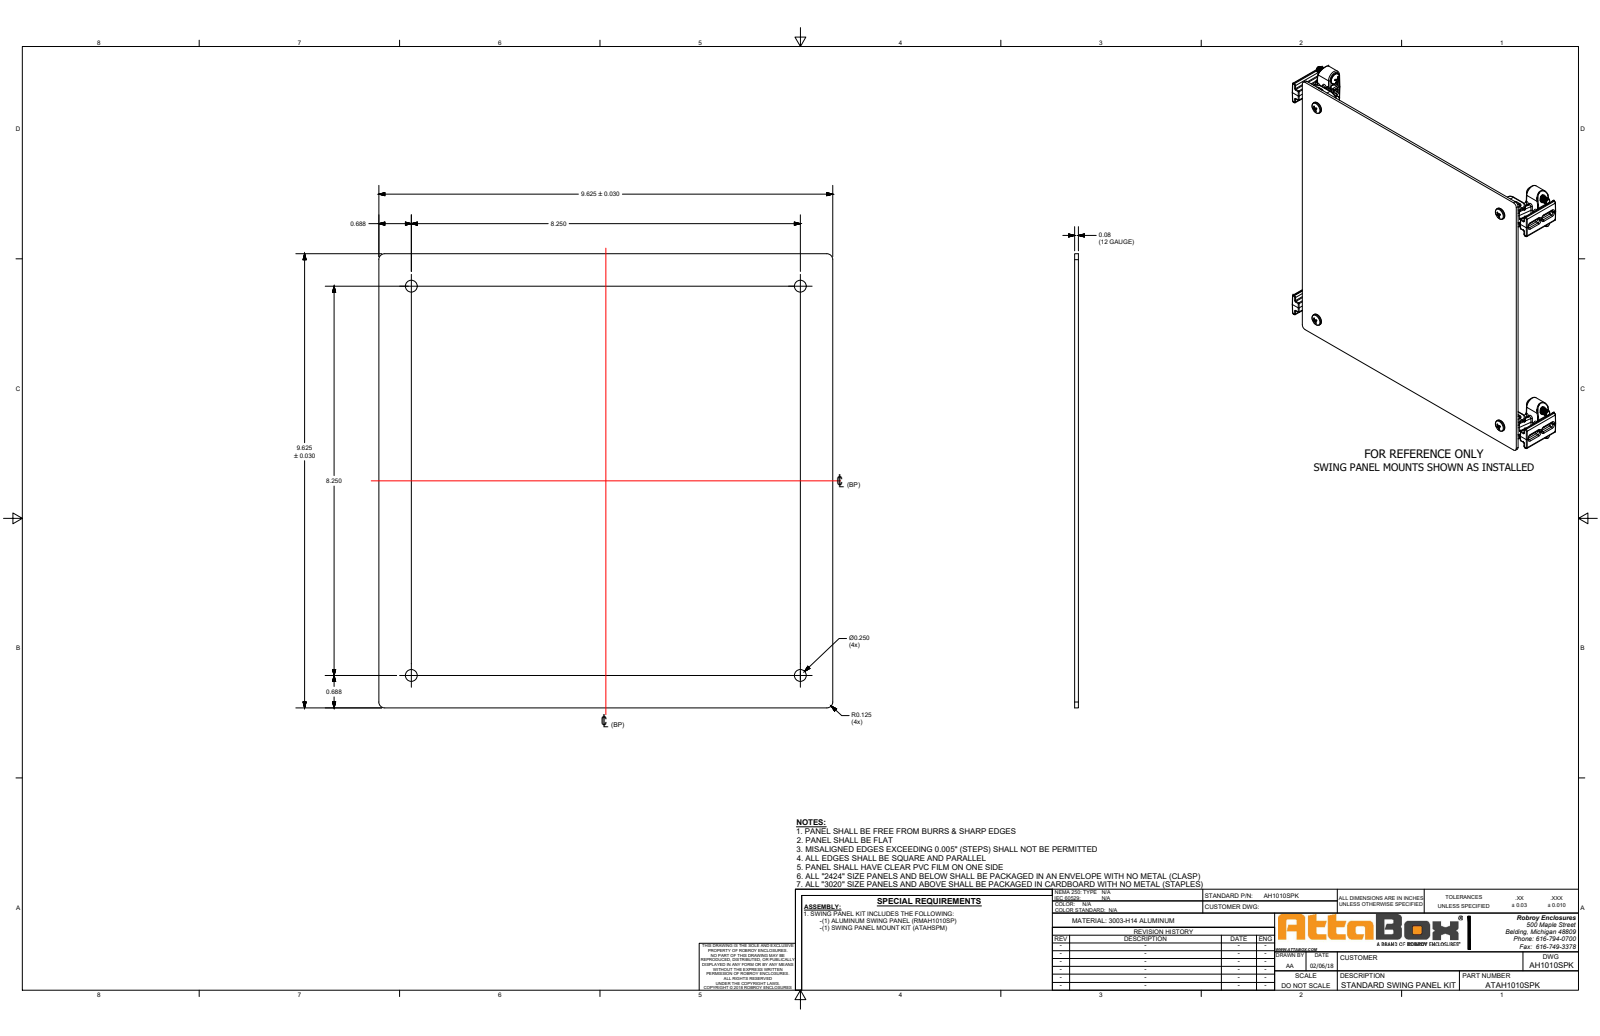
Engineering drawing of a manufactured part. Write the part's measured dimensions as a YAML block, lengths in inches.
part_name: "AH1010SPK"
step_written_by: "SolidWorks 2019 (AUTOMOTIVE_DESIGN)"
units: inches
bodies: {solids: 33, faces: 2010, planar: 518, cylindrical: 736, other: 756}
overall_size: [10.559, 9.625, 1.448]
volume: 10.48
surface_area: 245.7
round_holes:
  - {diameter: 0.156, count: 8}
  - {diameter: 0.25, count: 8}
round_bosses_or_shafts:
  - {diameter: 0.373, count: 8}
  - {diameter: 0.262, count: 8}
  - {diameter: 0.19, count: 8}
partial_cylinders:
  - {radius: 0.035, count: 248}
  - {radius: 0.02, count: 124}
  - {radius: 0.065, count: 54}
  - {radius: 0.015, count: 30}
  - {radius: 0.045, count: 16}
  - {radius: 0.05, count: 16}
  - {radius: 0.025, count: 12}
  - {radius: 0.9, count: 8}
face_to_face_distances: [0.08, 0.14, 8.25, 0.5, 0.51, 0.59, 0.3, 0.36, 0.863, 10.559]
hole_center_spacings: [8.25, 0.875, 8.25, 11.667, 7.375, 9.125]
